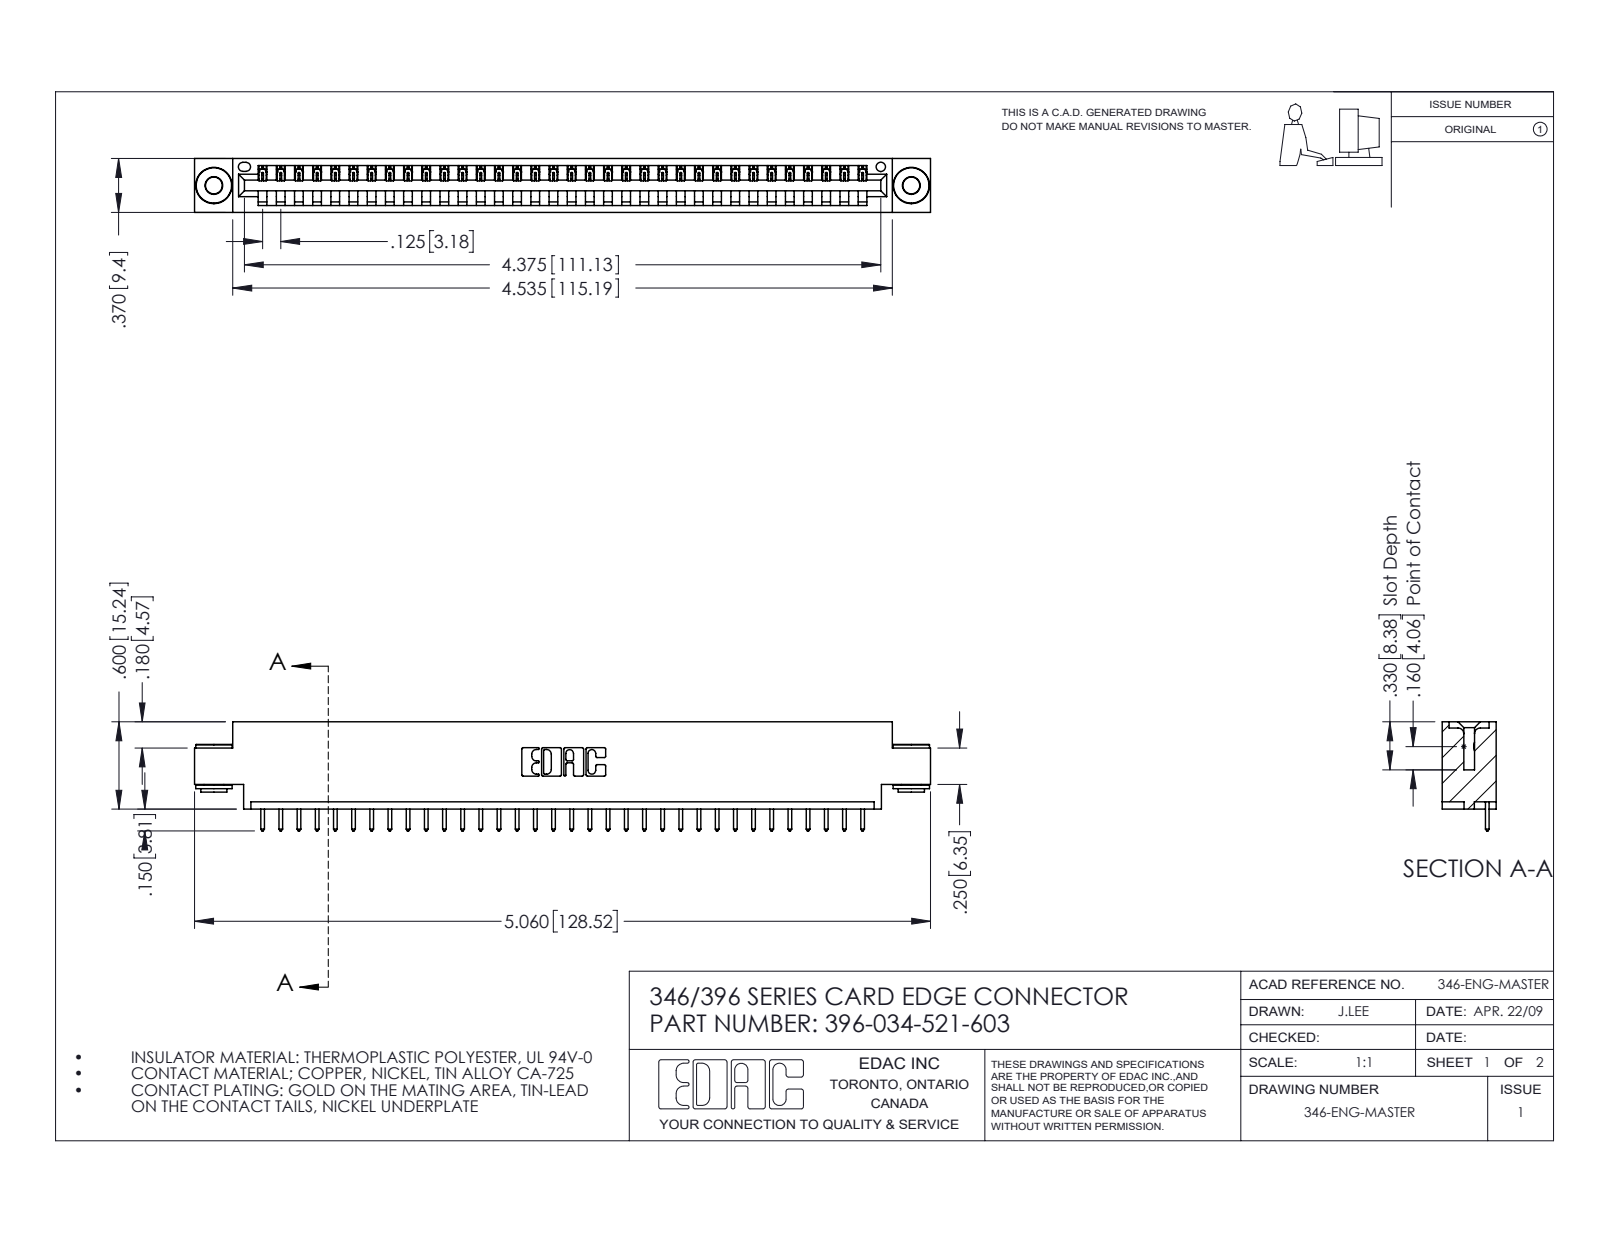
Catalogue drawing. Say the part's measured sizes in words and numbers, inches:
The part is named "346 Part_0.170 Offset - 0.156 Dia-TH; 345-250-002_345-250-002-102; 345-292-001_345-293-121; 396-034-521-603". Its 3-D file was written by "SolidWorks 2016 (CONFIG_CONTROL_DESIGN)". It is 37 solids with 2136 faces: 1450 planar, 678 cylindrical and 8 other. Overall it measures 5.06 by 0.75 by 0.37 inches. Its volume is 0.733 cubic inches and its surface area 23.14 square inches. Round holes: 2 of diameter 0.116, 2 of diameter 0.156, 1 of diameter 0.064. Round bosses or shafts: 2 of diameter 0.25, 2 of diameter 0.18, 2 of diameter 0.136. Partial cylindrical surfaces (rounded edges, fillets, slot ends): 68 of radius 0.006, 68 of radius 0.01, 22 of radius 0.01, 6 of radius 0.007, 6 of radius 0.031, 3 of radius 0.026, 2 of radius 0.031, 2 of radius 0.04. The main face-to-face distances are 0.048, 0.322, 0.37, 0.25, 0.025, 0.072, 0.298, 0.148, 0.222, 0.1. The hole center spacings are 0.246, 4.587, 4.795.
